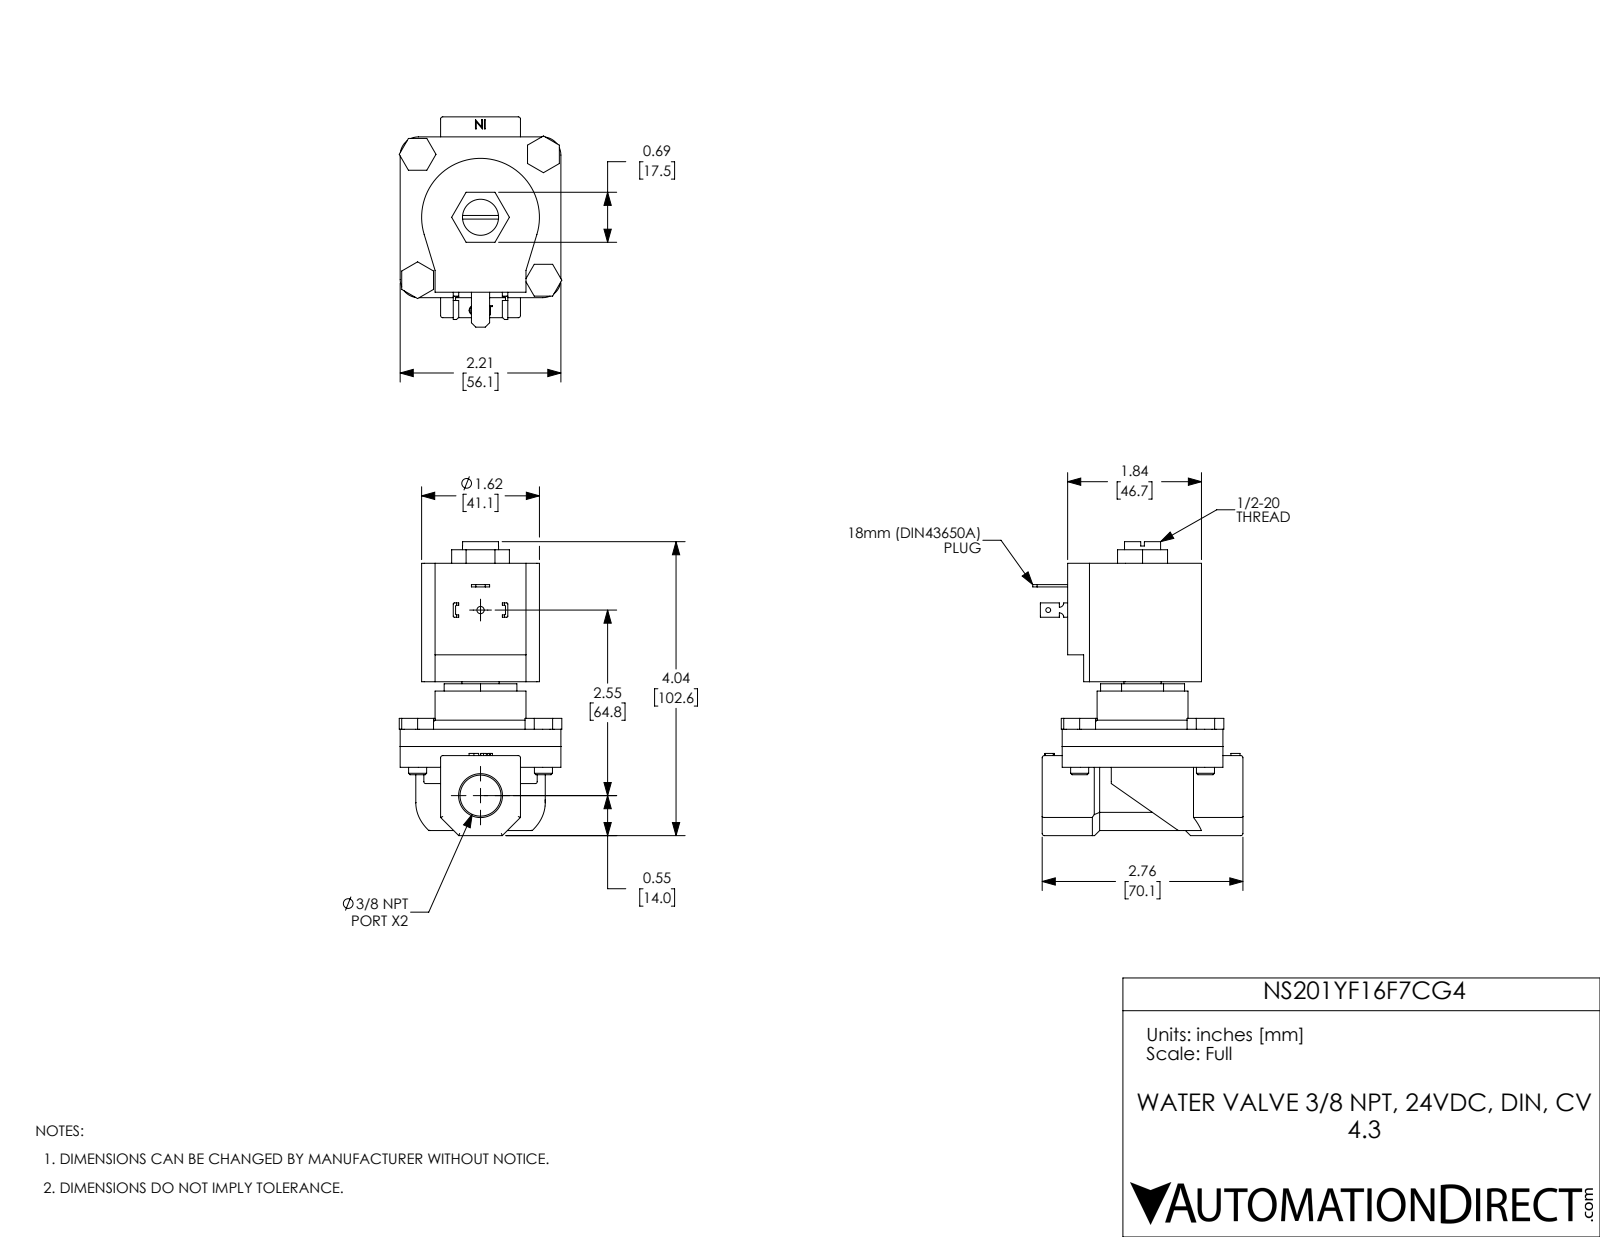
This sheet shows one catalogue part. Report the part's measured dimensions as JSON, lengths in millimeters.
{"part_name": "NS201YF16F7CG4", "step_written_by": "SolidWorks 2017 (AUTOMOTIVE_DESIGN)", "units": "millimeters", "bodies": {"solids": 11, "faces": 330, "planar": 196, "cylindrical": 99, "other": 35}, "overall_size": [102.6, 73.4, 56.8], "volume_mm3": 164700, "surface_area_mm2": 40680, "round_holes": [[6.4, 4], [1.7, 1], [2.5, 1], [12.6, 1], [13, 1], [14.3, 1], [29.3, 1]], "round_bosses_or_shafts": [[6.3, 4], [31.8, 1]], "partial_cylinders_radius": [[0.8, 15], [0.4, 8], [6.4, 4], [1.5, 2], [20.6, 1], [22.6, 1]], "face_to_face_distances": [6, 6, 64, 64, 57.9, 14.1, 42, 63.1, 7.3, 7.3], "hole_center_spacings": [31.1, 43.9, 62.1, 64.8]}
